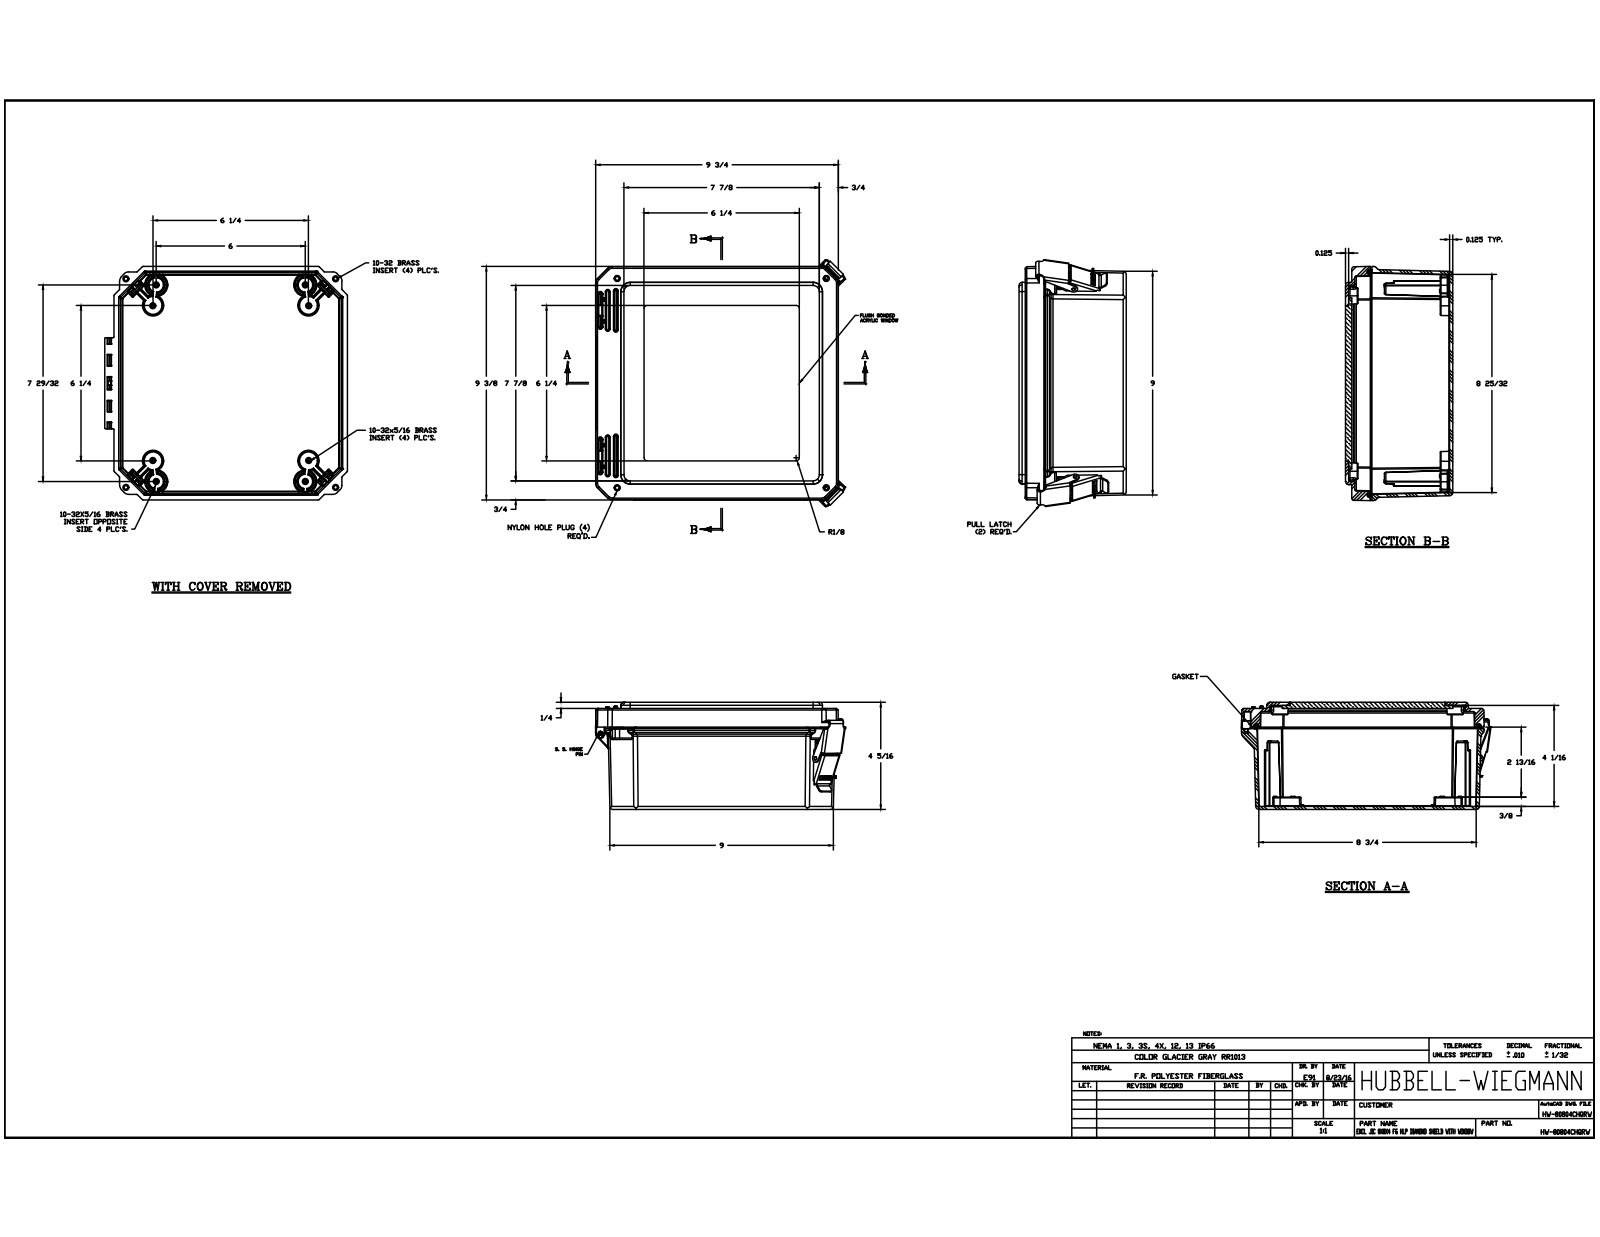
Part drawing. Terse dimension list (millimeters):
name: DSW80804HPL_STP; DS080804BOX; BRASS INSERT-(; BRASS INSERT-(_1 (+8 more)
written by: Autodesk Inventor 2017 (AUTOMOTIVE_DESIGN)
unit: mm
bodies: 34 solids, 2169 faces (766 planar, 855 cylindrical, 548 other)
size: 256.41 × 255.16 × 109.53
volume: 928 882 mm³; area: 491 720 mm²
holes: 16× ⌀3.96, 9× ⌀3.43, 8× ⌀3.86, 4× ⌀3.81, 4× ⌀6.4, 4× ⌀6.43, 2× ⌀3.43, 2× ⌀5.56, 2× ⌀5.77, 2× ⌀7.94, 2× ⌀9.52, 1× ⌀3.48
bosses: 16× ⌀6.25, 4× ⌀22.1, 4× ⌀7.62, 4× ⌀5.3, 3× ⌀3.43, 2× ⌀11.05
rounds: 109× R0.25, 80× R0.13, 65× R0.51, 62× R0.76, 33× R1.52, 28× R1.59, 26× R2.29, 26× R3.17
face distances: 3.17, 106.36, 103.82, 100.65, 106.31, 109.53, 5.71, 3.15, 6.35, 6.4
hole spacings: 6.35, 158.75, 21.27, 31.3, 179.1, 179.82, 183.14, 188.22
